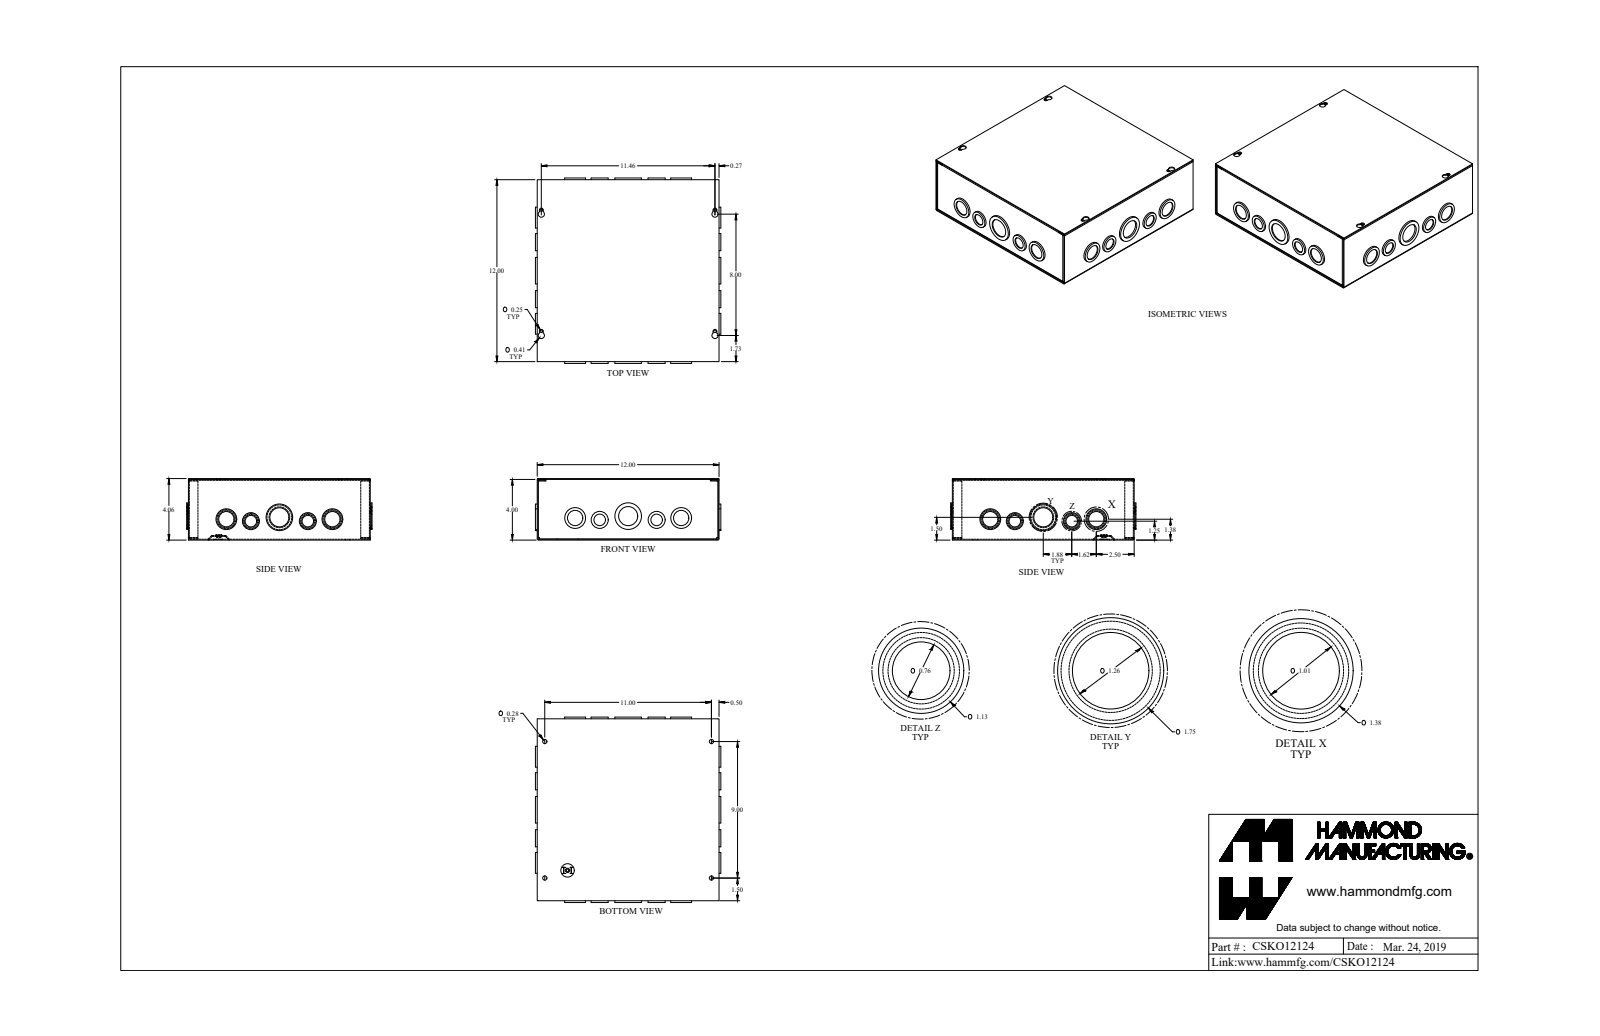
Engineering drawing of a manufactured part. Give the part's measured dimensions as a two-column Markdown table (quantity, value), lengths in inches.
| quantity | value |
| --- | --- |
| part name | CSKO12124_Default |
| STEP written by | SolidWorks 2019 (CONFIG_CONTROL_DESIGN) |
| units | inches |
| bodies | 4 solids, 445 faces (205 planar, 232 cylindrical, 8 other) |
| overall size | 12.234 × 12.234 × 4.057 |
| volume | 30.09 in³ |
| surface area | 1 067 in² |
| round holes (diameter × count) | 1.011 × 8, 1.261 × 6, 0.17 × 5, 0.281 × 4, 0.761 × 4, 1.636 × 2, 0.5 × 1 |
| round bosses / shafts (diameter × count) | 1.125 × 6, 1.375 × 5, 0.875 × 4, 1.75 × 2, 1.125 × 2, 0.875 × 2, 1.375 × 1, 0.492 × 1 |
| partial cylindrical surfaces (radius × count) | 0.029 × 12, 0.086 × 12, 0.057 × 8, 0.125 × 4, 0.203 × 4 |
| main face-to-face distances | 0.057, 4, 3.943, 11.943, 4.057, 12, 11.886, 0.114, 0.08, 3.863 |
| hole center spacings | 0.55, 1.625, 1.896, 3.502, 5.381, 8.503, 11.241, 14.084 |
